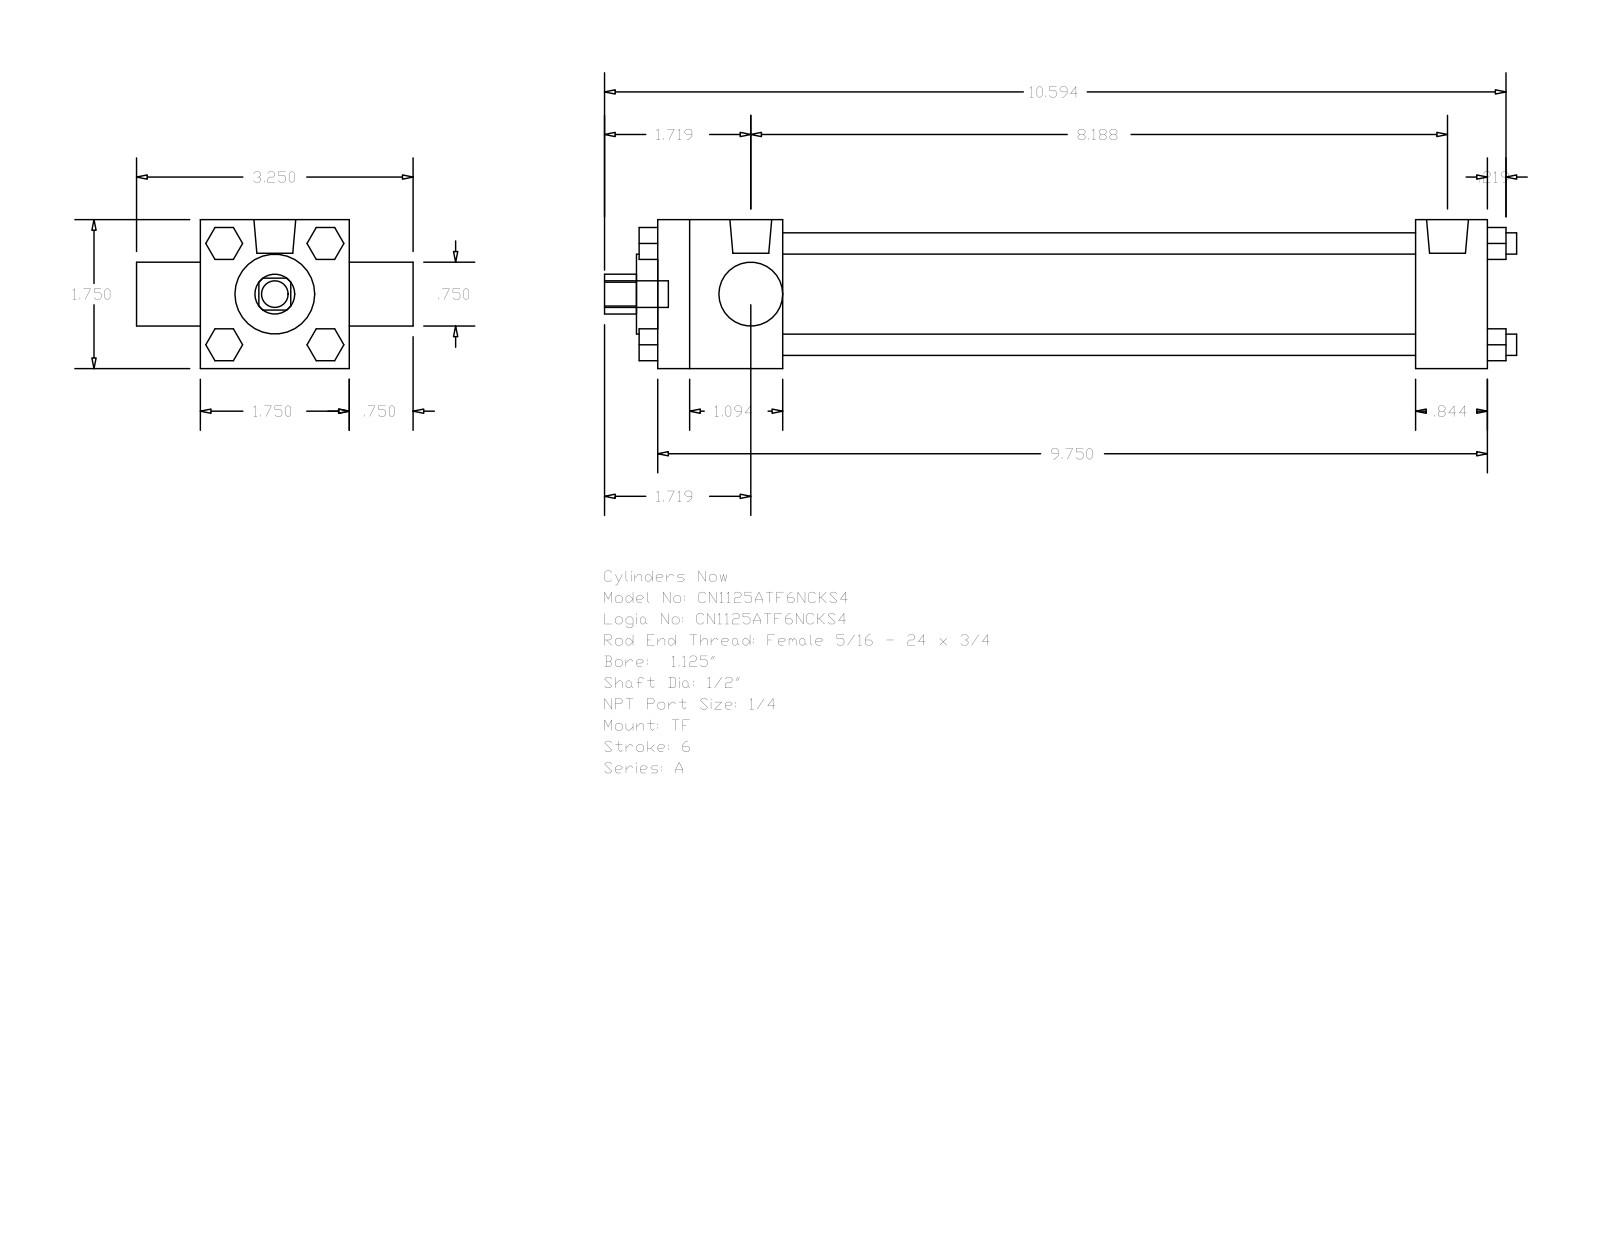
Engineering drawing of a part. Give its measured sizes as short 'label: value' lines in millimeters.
name: A_TF__0112_0.5
written by: GSSL Pune (CONFIG_CONTROL_DESIGN)
unit: mm
bodies: 0 solids, 120 faces (92 planar, 28 cylindrical, 0 other)
size: 272.26 × 82.55 × 44.45
holes: 1× ⌀12.7, 1× ⌀19.05, 1× ⌀23.81, 1× ⌀31.88
bosses: 4× ⌀6.35, 3× ⌀5.56, 2× ⌀12.49, 1× ⌀7.94
rounds: 1× R5.94
face distances: 44.46, 247.64, 226.21, 21.43, 37.3, 188.91, 210.34, 19.04, 63.5, 9.53
